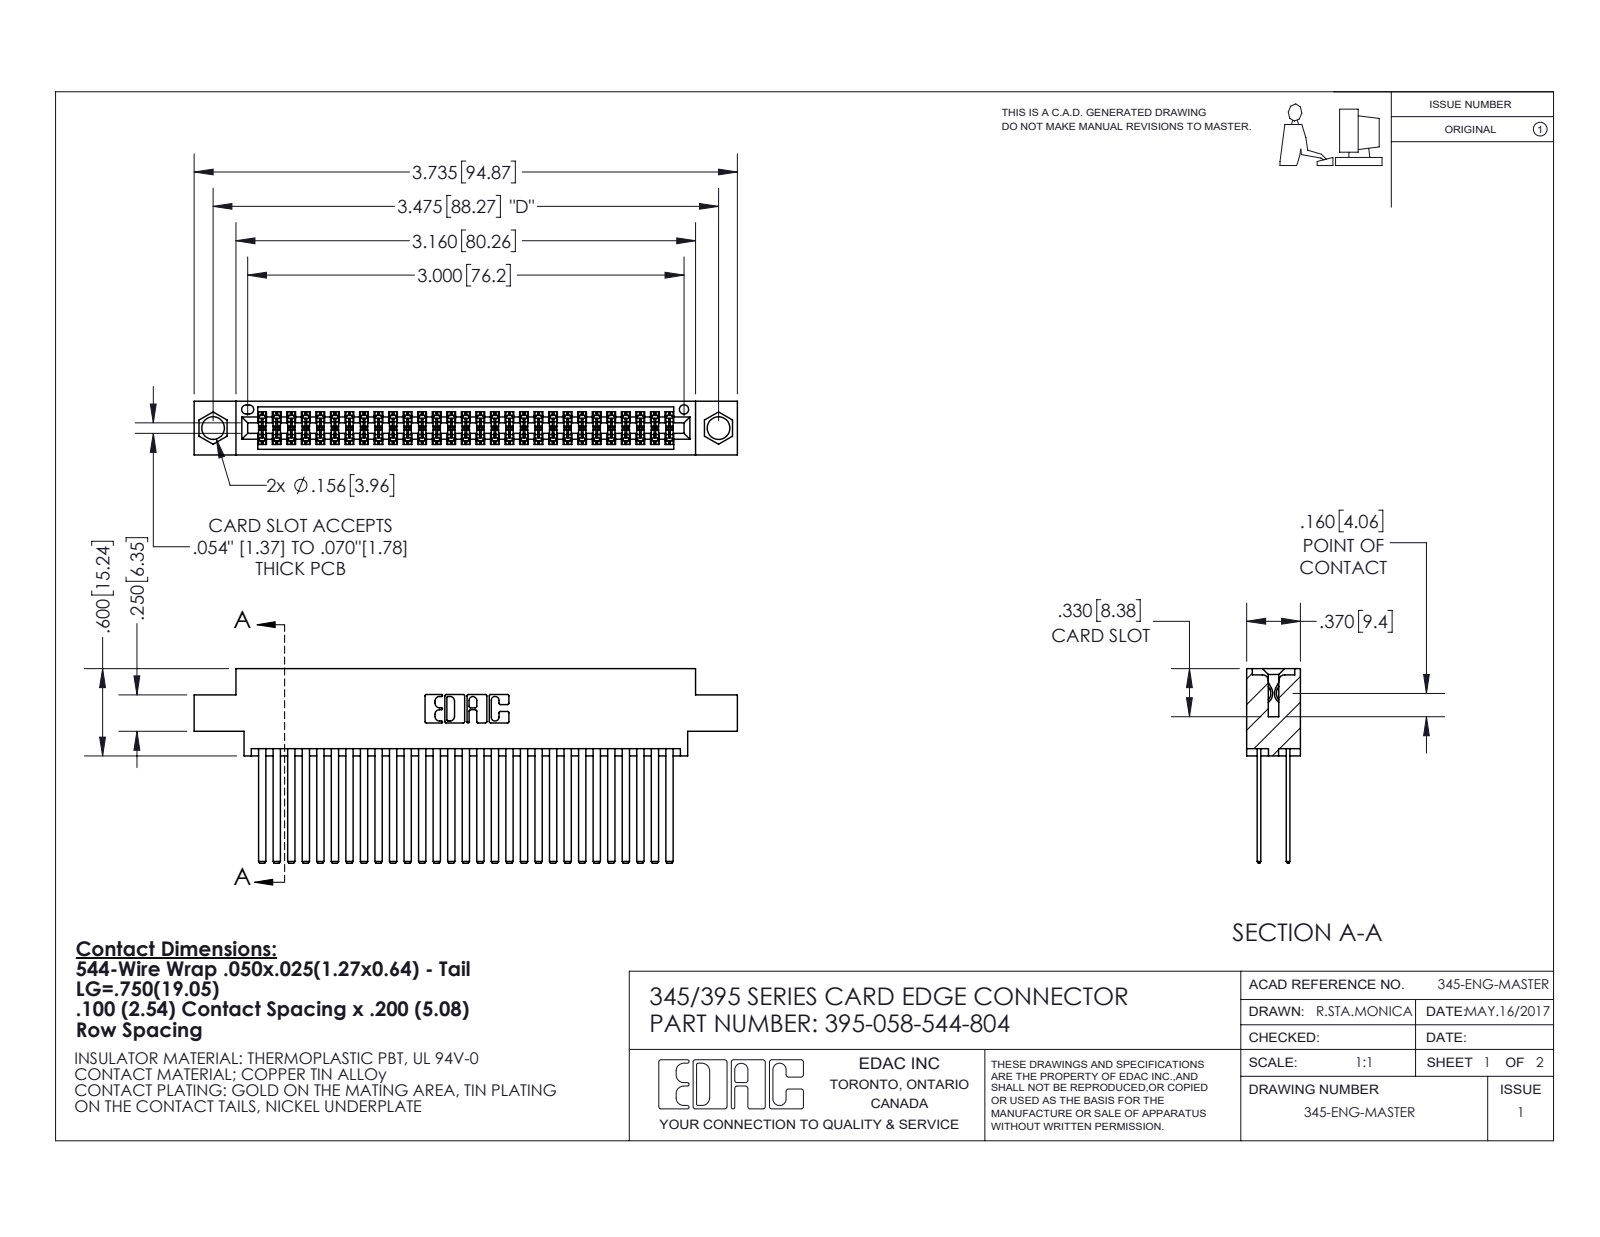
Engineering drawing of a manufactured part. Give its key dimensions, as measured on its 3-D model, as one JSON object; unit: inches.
{"part_name": "345-292-001_345-293-144; 345 Part_0.170 Offset - 0.156 Dia-TI; 395-058-544-804", "step_written_by": "SolidWorks 2020 (CONFIG_CONTROL_DESIGN)", "units": "inches", "bodies": {"solids": 59, "faces": 2696, "planar": 1780, "cylindrical": 916, "other": 0}, "overall_size": [3.735, 1.337, 0.37], "volume_in3": 0.591, "surface_area_in2": 25.49, "round_holes": [[0.156, 2], [0.064, 1]], "partial_cylinders_radius": [[0.006, 116], [0.01, 22], [0.007, 6], [0.031, 6], [0.026, 3], [0.014, 2], [0.019, 2], [0.022, 2]], "face_to_face_distances": [0.2, 0.025, 0.072, 0.298, 0.098, 0.272, 0.225, 0.175, 0.37, 0.15], "hole_center_spacings": [0.27, 3.24, 3.475]}
